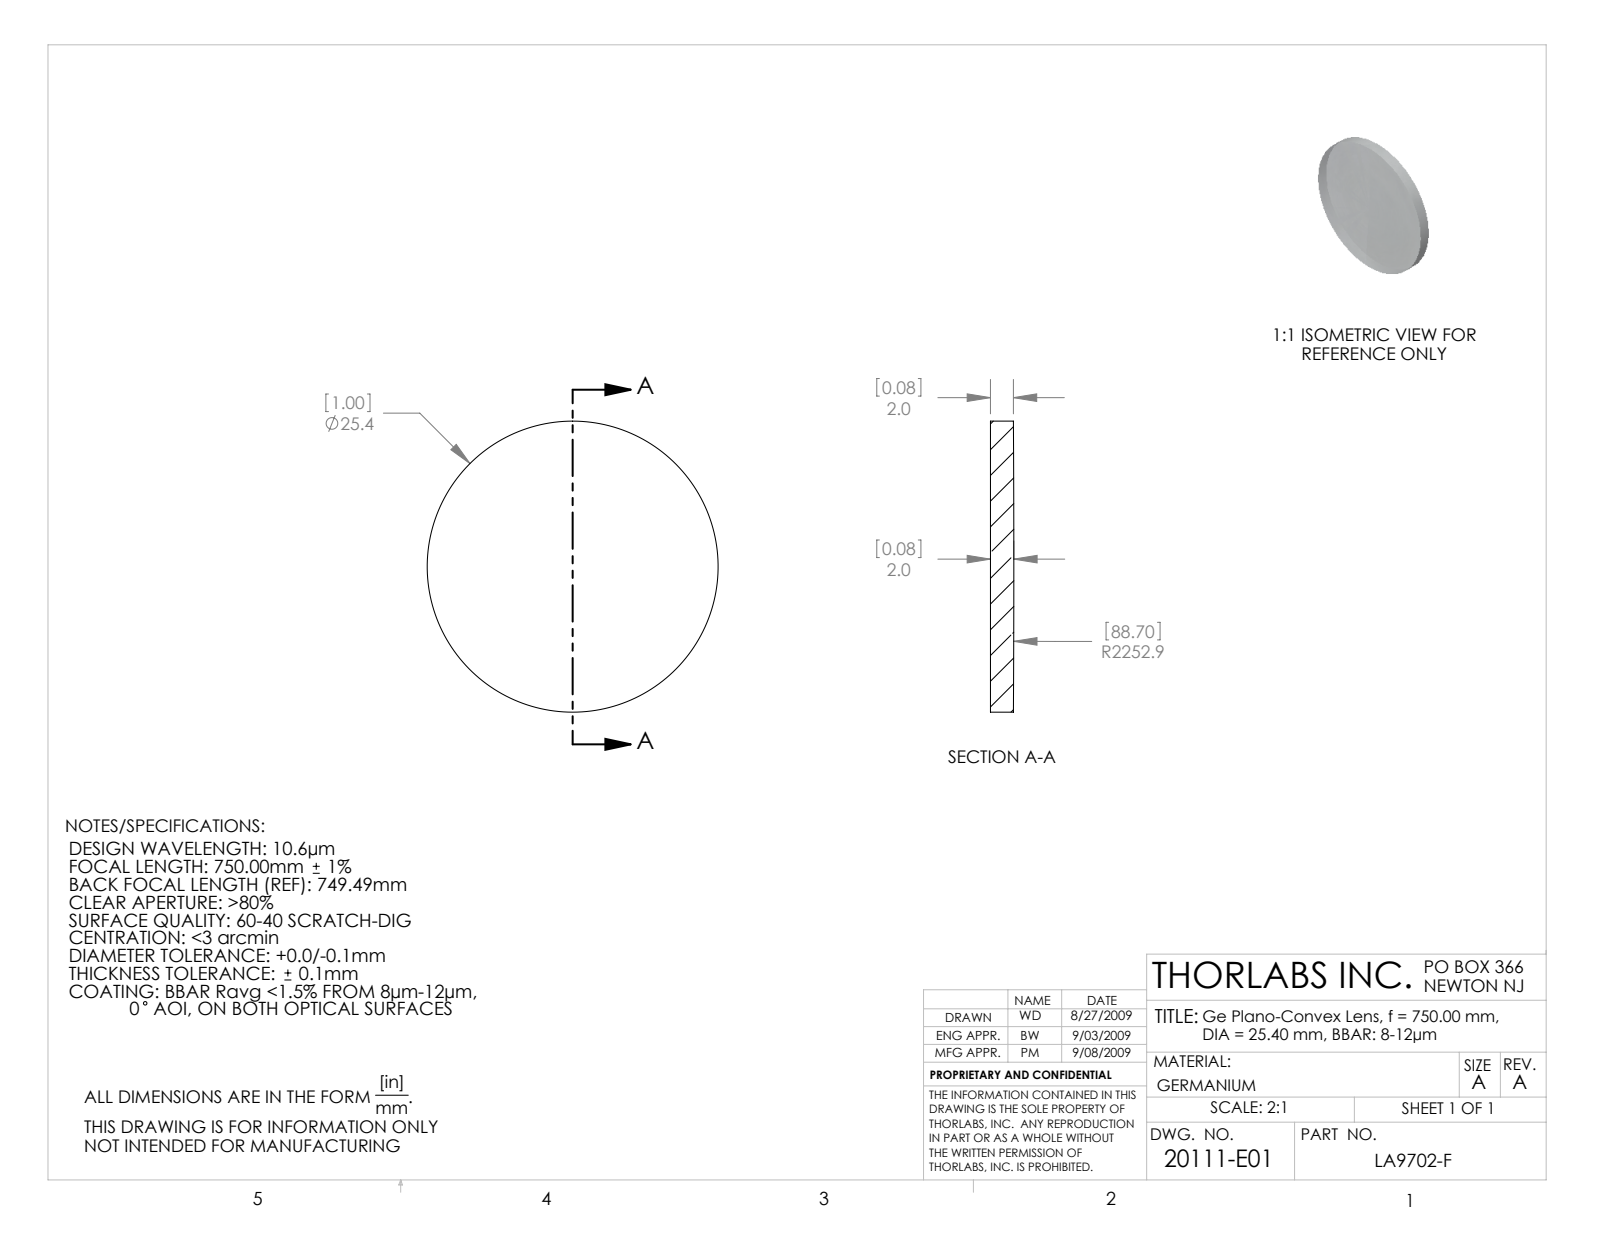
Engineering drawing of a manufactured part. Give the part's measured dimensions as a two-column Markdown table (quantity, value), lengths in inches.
| quantity | value |
| --- | --- |
| part name | 20111-E0W |
| STEP written by | SolidWorks 2007 (CONFIG_CONTROL_DESIGN) |
| units | inches |
| bodies | 1 solid, 5 faces (1 planar, 2 cylindrical, 2 other) |
| overall size | 1 × 1 × 0.08 |
| volume | 0.063 in³ |
| surface area | 1.818 in² |
| round bosses / shafts (diameter × count) | 1 × 1 |
